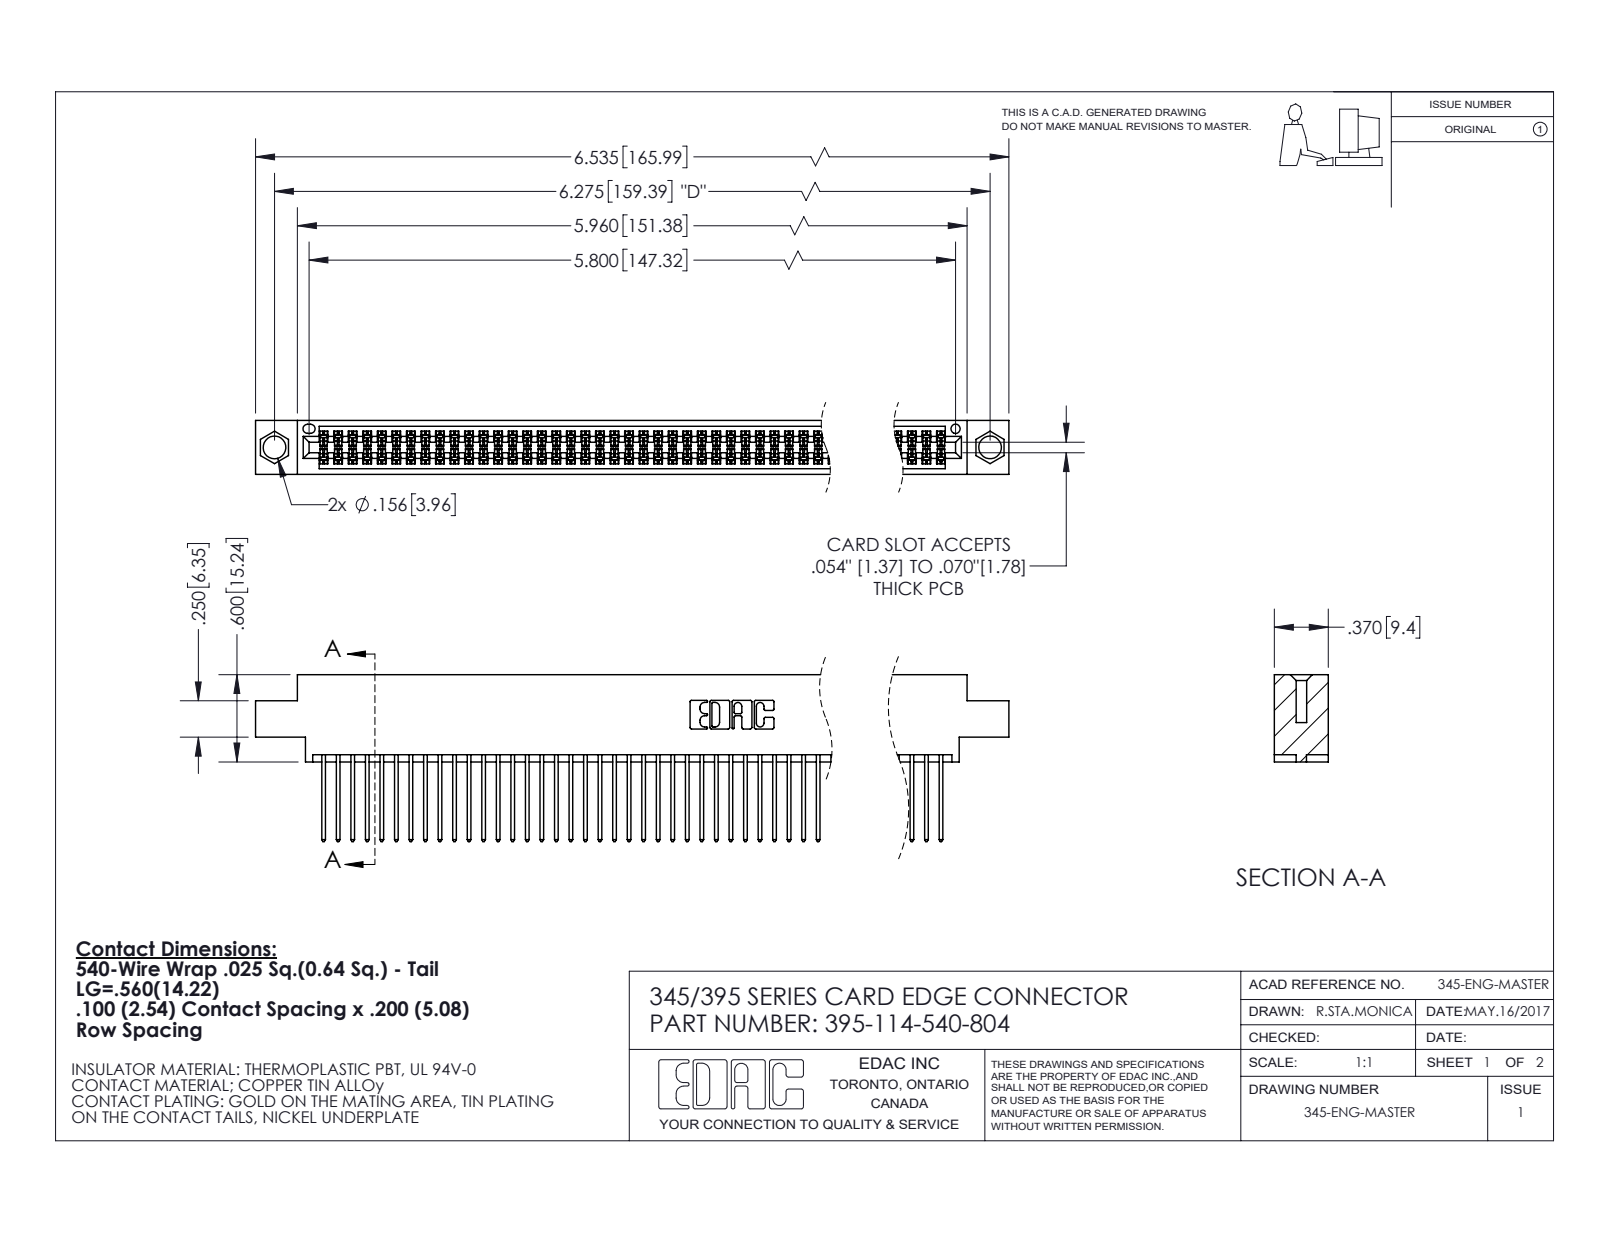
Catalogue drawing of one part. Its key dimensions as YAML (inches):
part_name: "395-114-540-804; 345 Part_0.170 Offset - 0.156 Dia-TI; 345-292-001_345-293-140"
step_written_by: "SolidWorks 2020 (CONFIG_CONTROL_DESIGN)"
units: inches
bodies: {solids: 115, faces: 5844, planar: 3860, cylindrical: 1984, other: 0}
overall_size: [6.535, 1.147, 0.37]
volume: 1.005
surface_area: 41.3
round_holes:
  - {diameter: 0.156, count: 2}
  - {diameter: 0.064, count: 1}
partial_cylinders:
  - {radius: 0.006, count: 228}
  - {radius: 0.01, count: 114}
  - {radius: 0.01, count: 22}
  - {radius: 0.007, count: 6}
  - {radius: 0.031, count: 6}
  - {radius: 0.026, count: 3}
  - {radius: 0.014, count: 2}
  - {radius: 0.019, count: 2}
face_to_face_distances: [0.072, 0.298, 0.2, 0.098, 0.272, 0.025, 0.37, 0.225, 0.175, 0.149]
hole_center_spacings: [0.27, 6.039, 6.275]
